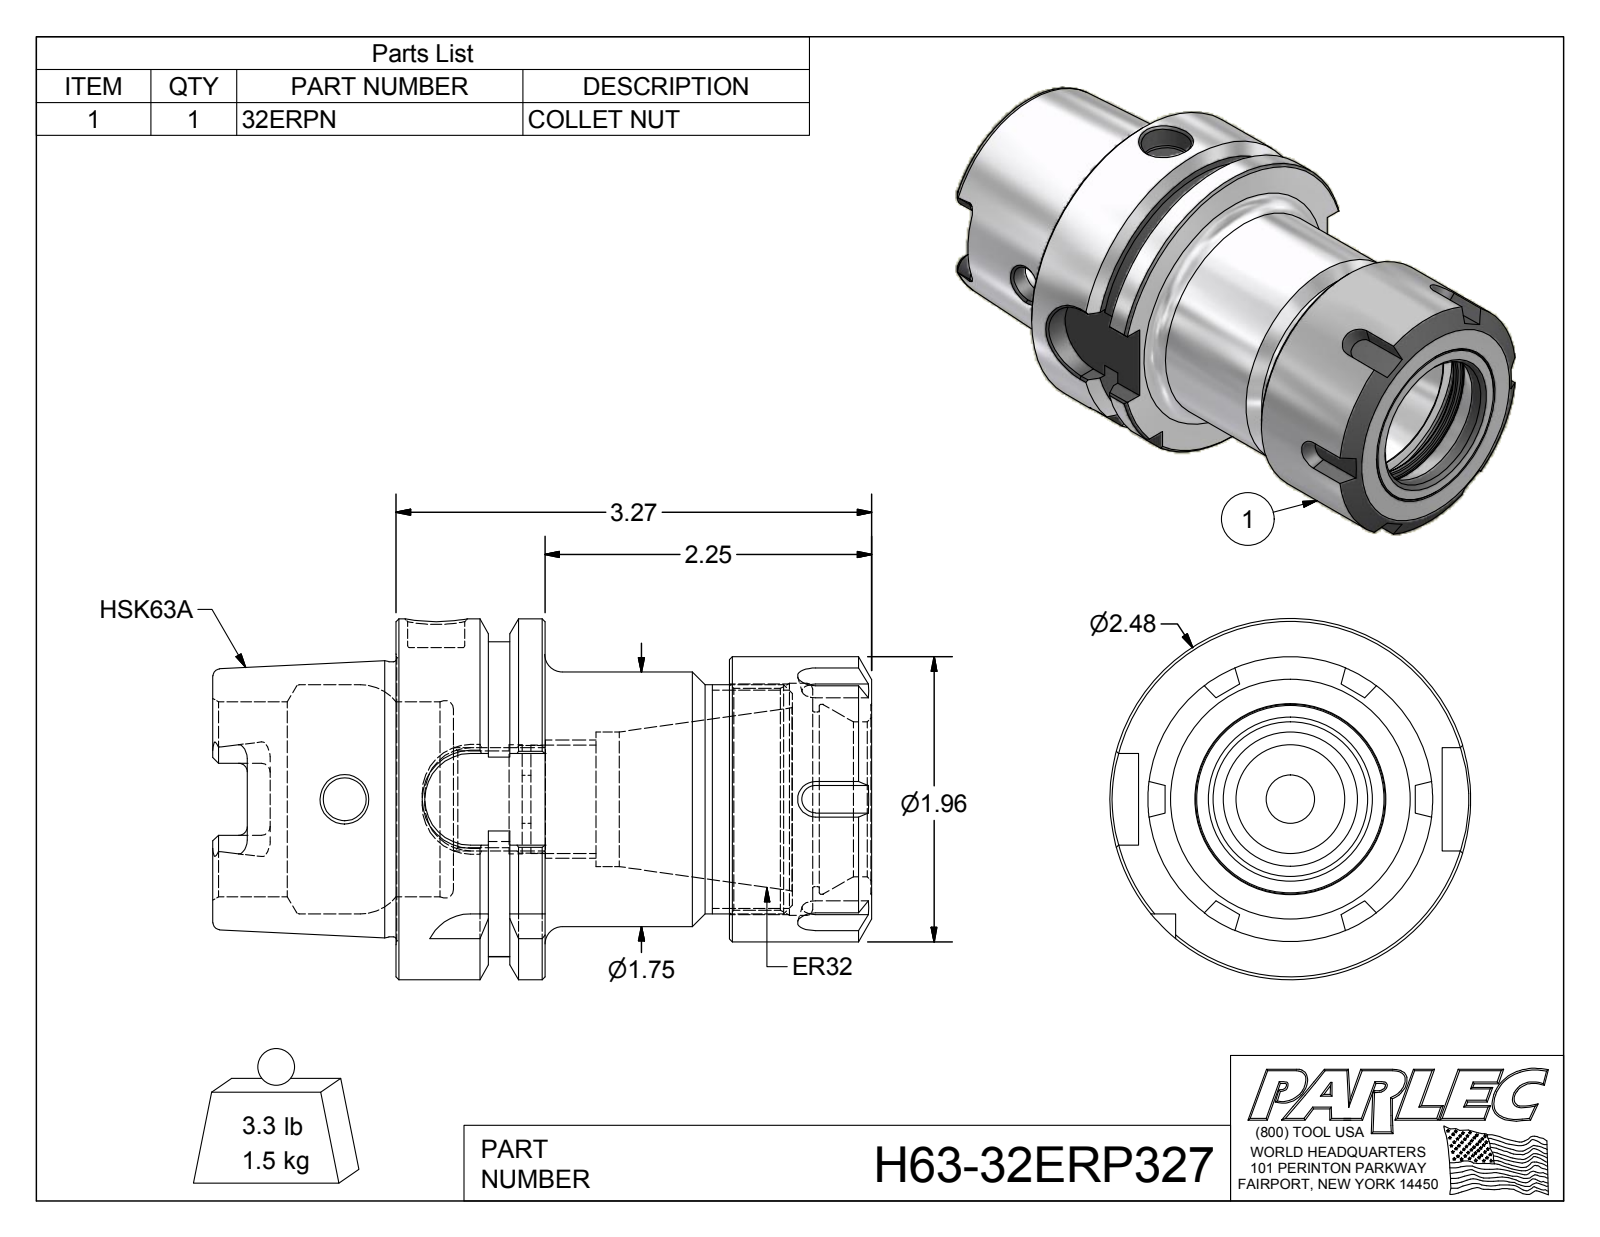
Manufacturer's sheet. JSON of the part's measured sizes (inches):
{"part_name": "H63-32ERP327; H63-32ER3-1; 32ERPN", "step_written_by": "Autodesk Inventor 2012 (AUTOMOTIVE_DESIGN)", "units": "inches", "bodies": {"solids": 2, "faces": 186, "planar": 76, "cylindrical": 42, "other": 68}, "overall_size": [4.53, 2.48, 2.48], "volume_in3": 8.668, "surface_area_in2": 62.64, "round_holes": [[0.295, 1], [0.331, 1], [0.394, 1], [0.666, 1], [0.745, 1], [0.749, 1], [0.925, 1], [1.063, 1], [1.2, 1], [1.305, 1], [1.339, 1], [1.523, 1]], "round_bosses_or_shafts": [[2.48, 1], [1.958, 1], [1.891, 1], [1.75, 1]], "partial_cylinders_radius": [[0.059, 6], [0.113, 4], [0.315, 4], [1.083, 1]], "face_to_face_distances": [1.024, 3.27, 2.246, 0.241, 0.389, 2.292, 1.269, 0.978, 0.394, 0.63]}
